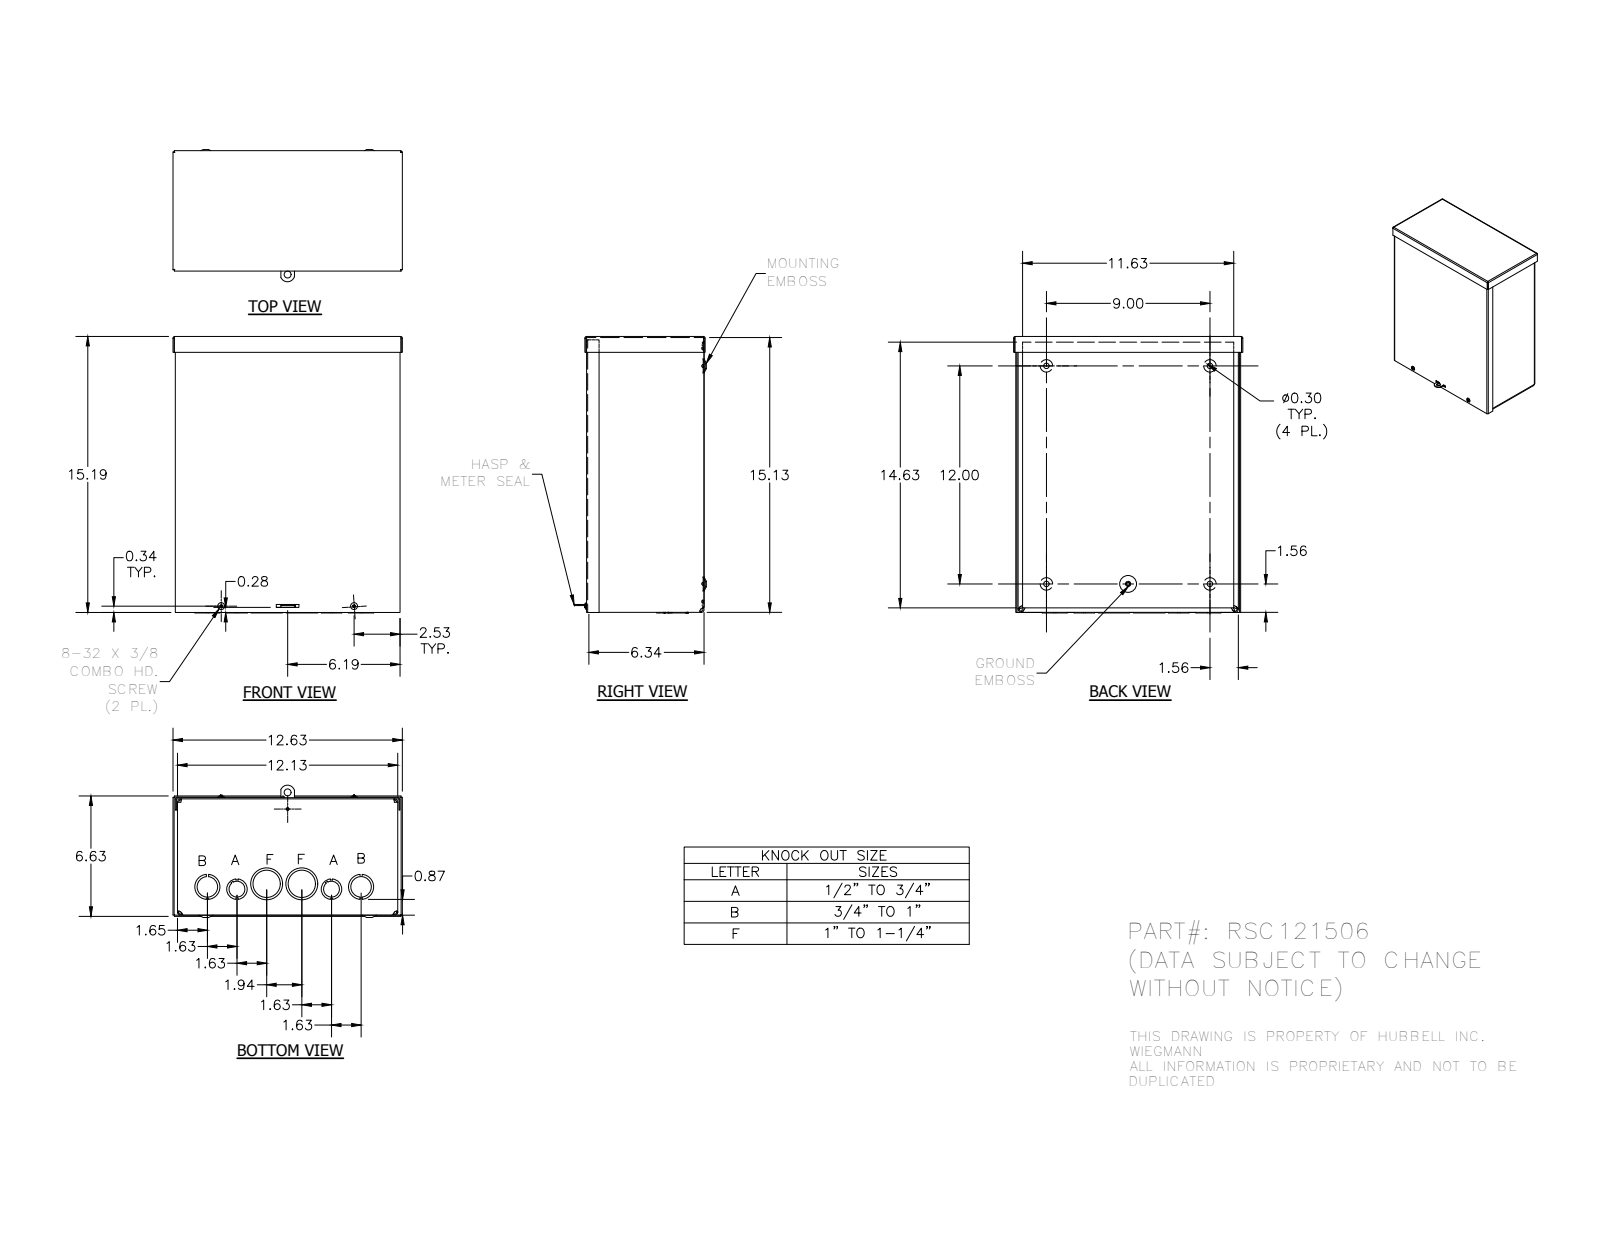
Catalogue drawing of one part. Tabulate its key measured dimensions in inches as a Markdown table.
| quantity | value |
| --- | --- |
| part name | RSC121506; RSC121506_WRAP; RSC1215_LID; RSC1206_CAP (+4 more) |
| STEP written by | Autodesk Inventor 2012 (AUTOMOTIVE_DESIGN) |
| units | inches |
| bodies | 7 solids, 551 faces (264 planar, 143 cylindrical, 144 other) |
| overall size | 15.281 × 12.625 × 7.125 |
| volume | 55.91 in³ |
| surface area | 1 824 in² |
| round holes (diameter × count) | 0.3 × 4, 0.313 × 4, 1.125 × 4, 0.125 × 2, 0.148 × 2, 0.875 × 2, 1.375 × 2, 1.5 × 2, 1.75 × 2, 0.156 × 1, 0.165 × 1, 0.375 × 1 |
| round bosses / shafts (diameter × count) | 0.384 × 2, 0.164 × 2, 0.229 × 1 |
| partial cylindrical surfaces (radius × count) | 0.01 × 14, 0.031 × 8, 0.093 × 8, 0.125 × 8, 0.187 × 8, 0.031 × 6, 0.025 × 5, 0.055 × 4 |
| main face-to-face distances | 0.062, 0.062, 6.249, 6.187, 12.126, 0.063, 6.312, 6.25, 15.126, 0.124 |
| hole center spacings | 1.356, 1.635, 1.656, 3.264, 3.582, 4.5, 5.203, 6.831 |
